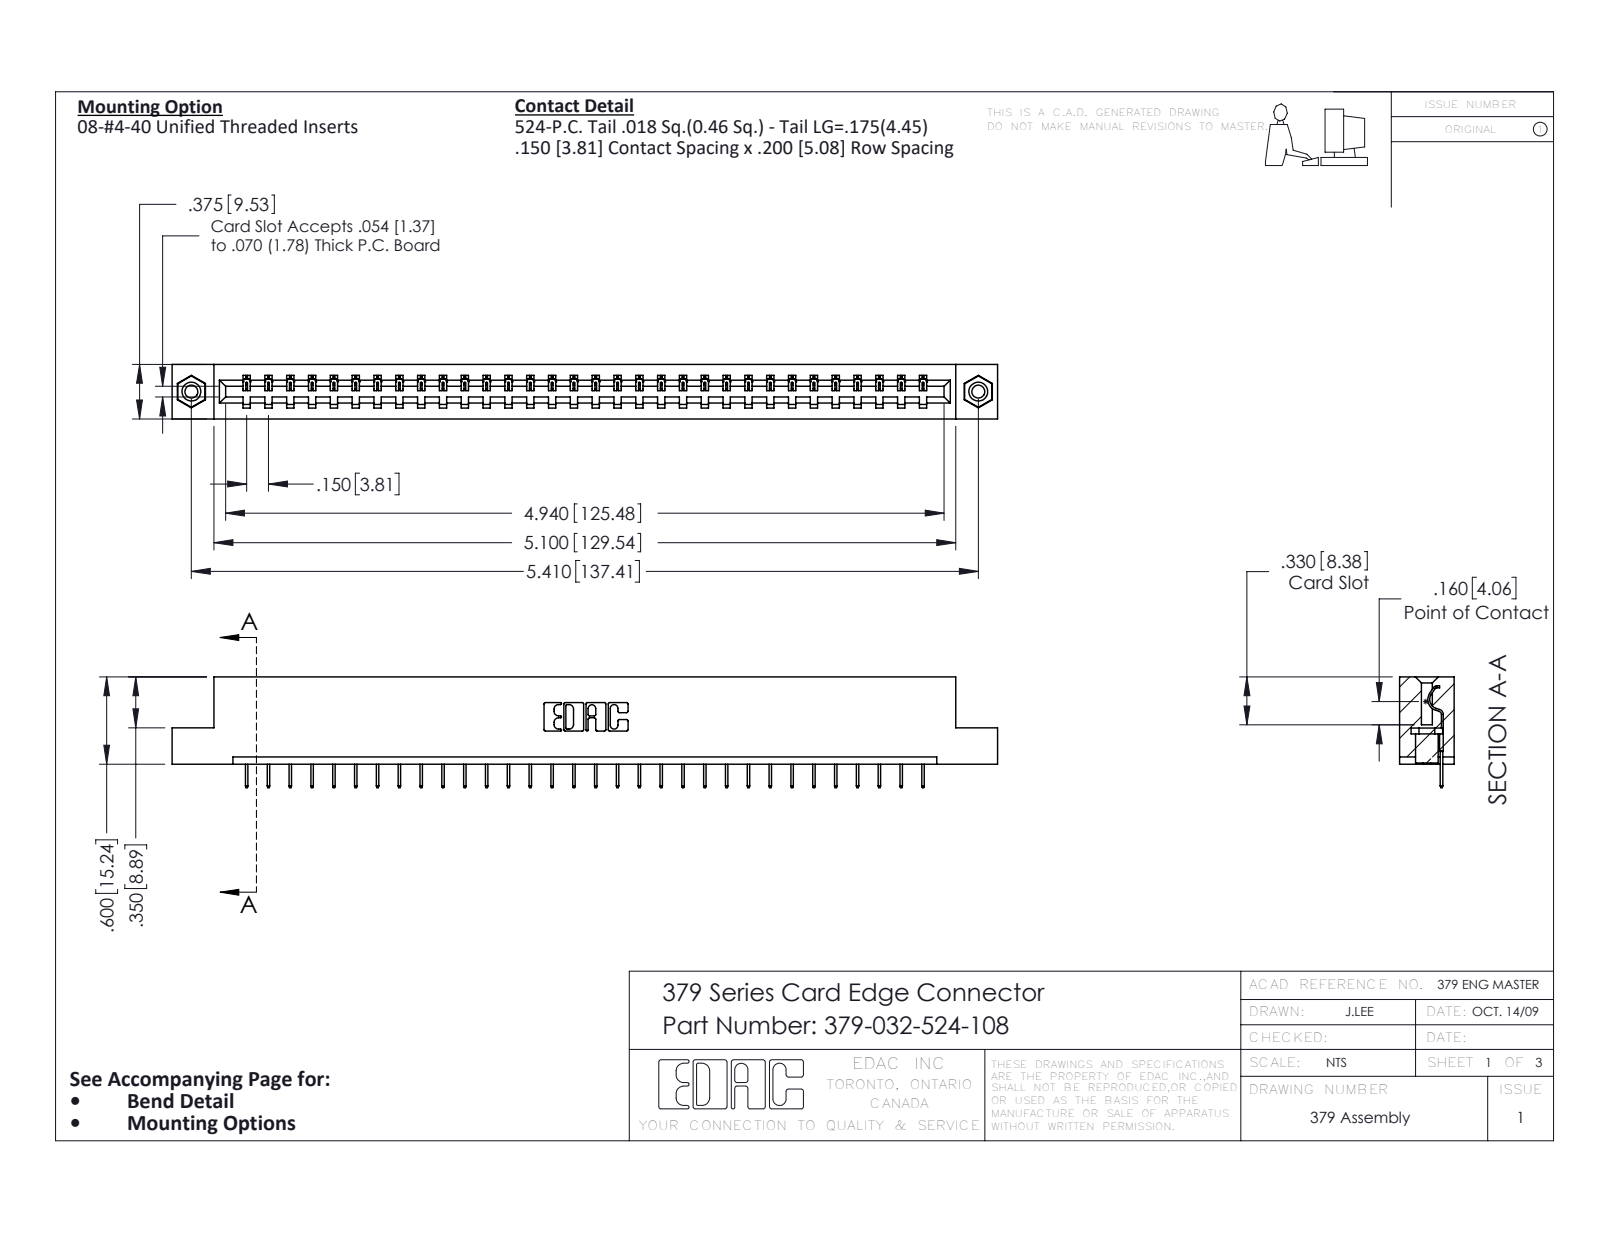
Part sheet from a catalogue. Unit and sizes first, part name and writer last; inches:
Units: inches
Overall size (bounding box): 5.675 × 0.762 × 0.375
Round holes (diameter × count): ⌀0.089 ×2, ⌀0.125 ×2, ⌀0.156 ×2
Round bosses / shafts (diameter × count): ⌀0.155 ×2
Partial cylindrical surfaces — rounded edges, fillets, slot ends (radius × count): R0.006 ×64, R0.01 ×22, R0.007 ×6, R0.031 ×6, R0.026 ×3, R0.014 ×1, R0.022 ×1, R0.024 ×1
Main face-to-face distances: 0.3, 0.075, 0.375, 0.225, 0.6, 0.55, 0.2, 0.15, 0.15, 0.15
Hole centre spacings: 5.41
Volume: 0.909 in³ · Surface area: 22.9 in²
Bodies: 35 solids, 2158 faces (1638 planar, 504 cylindrical, 16 other)
Part name (STEP PRODUCT): 345-250-001_345-250-003-102; 345-292-001_345-293-124; 379 Part_Flush - .156 Dia - TI; 379-032-524-108
STEP written by: SolidWorks 2016 (CONFIG_CONTROL_DESIGN)
